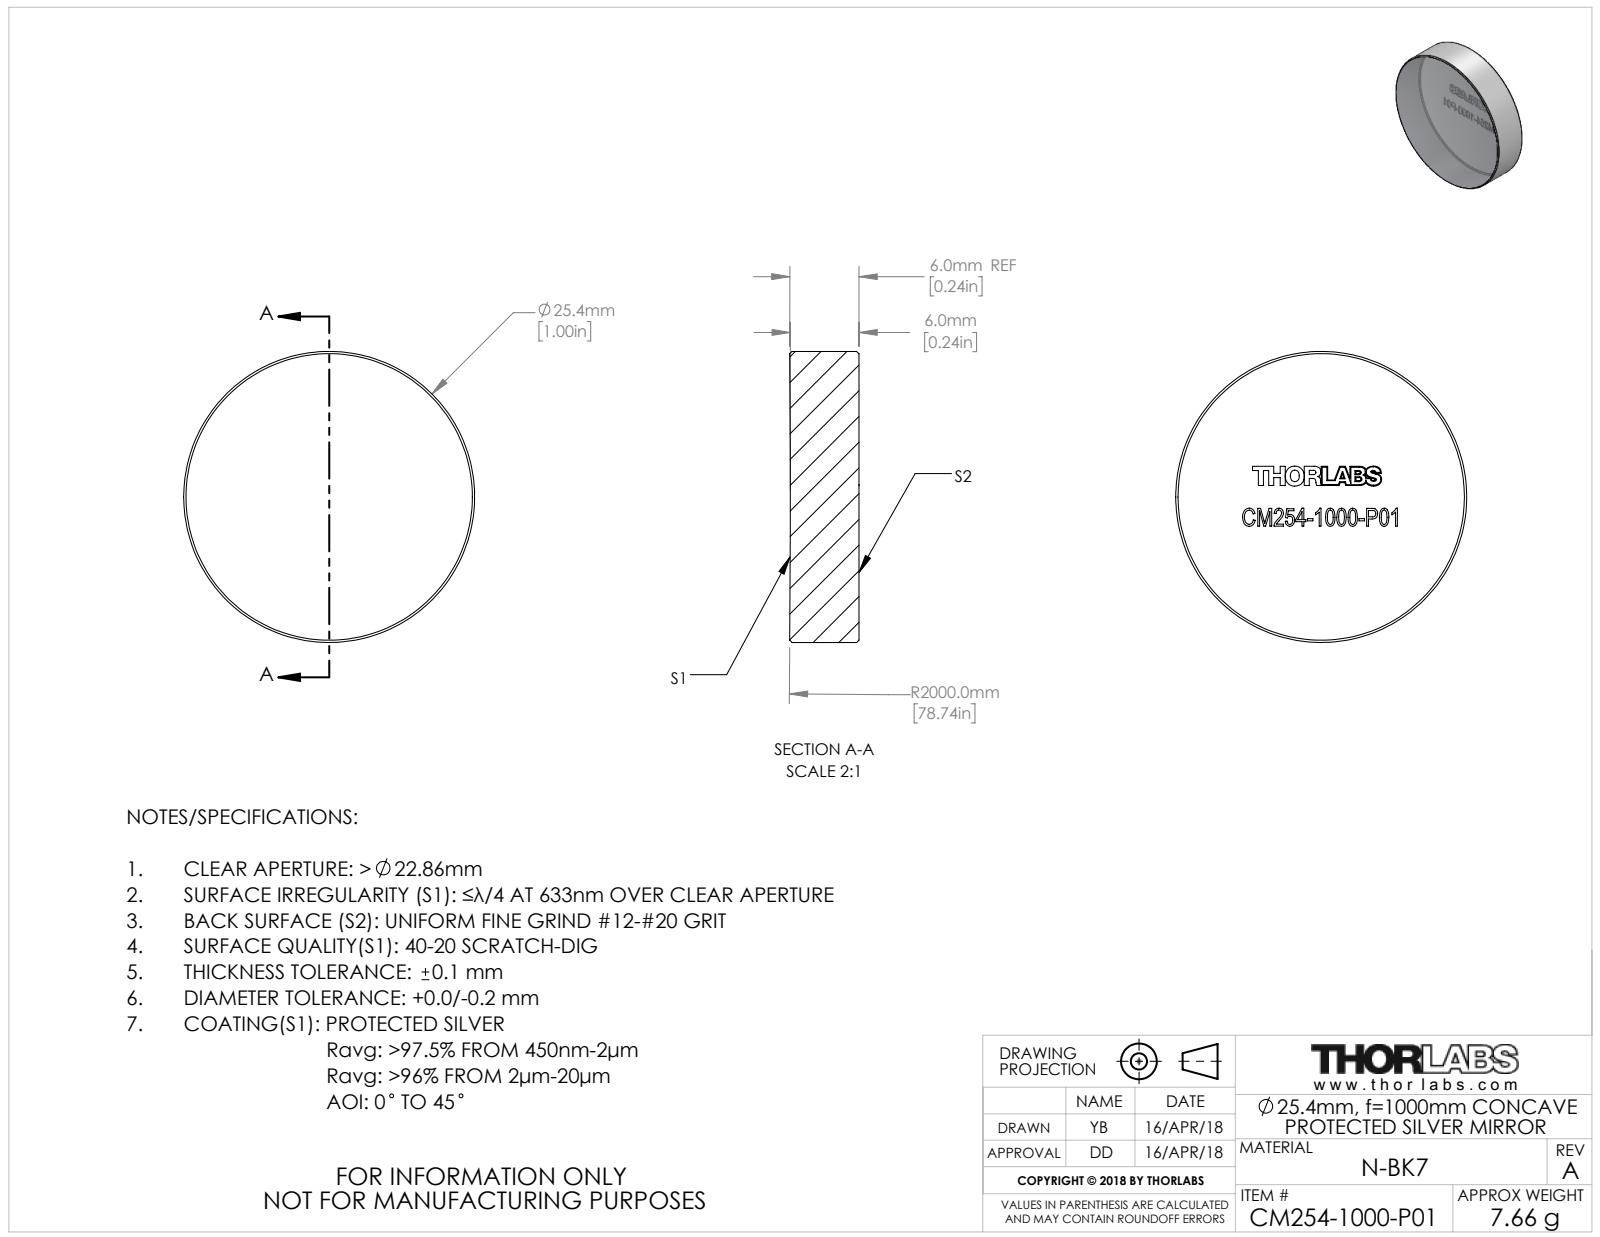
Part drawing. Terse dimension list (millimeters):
name: TTN153317-E0W
written by: SolidWorks 2018 (CONFIG_CONTROL_DESIGN)
unit: mm
bodies: 1 solid, 44 faces (36 planar, 2 cylindrical, 6 other)
size: 25.4 × 25.4 × 6.04
volume: 3 047 mm³; area: 1 477 mm²
bosses: 1× ⌀25.4
